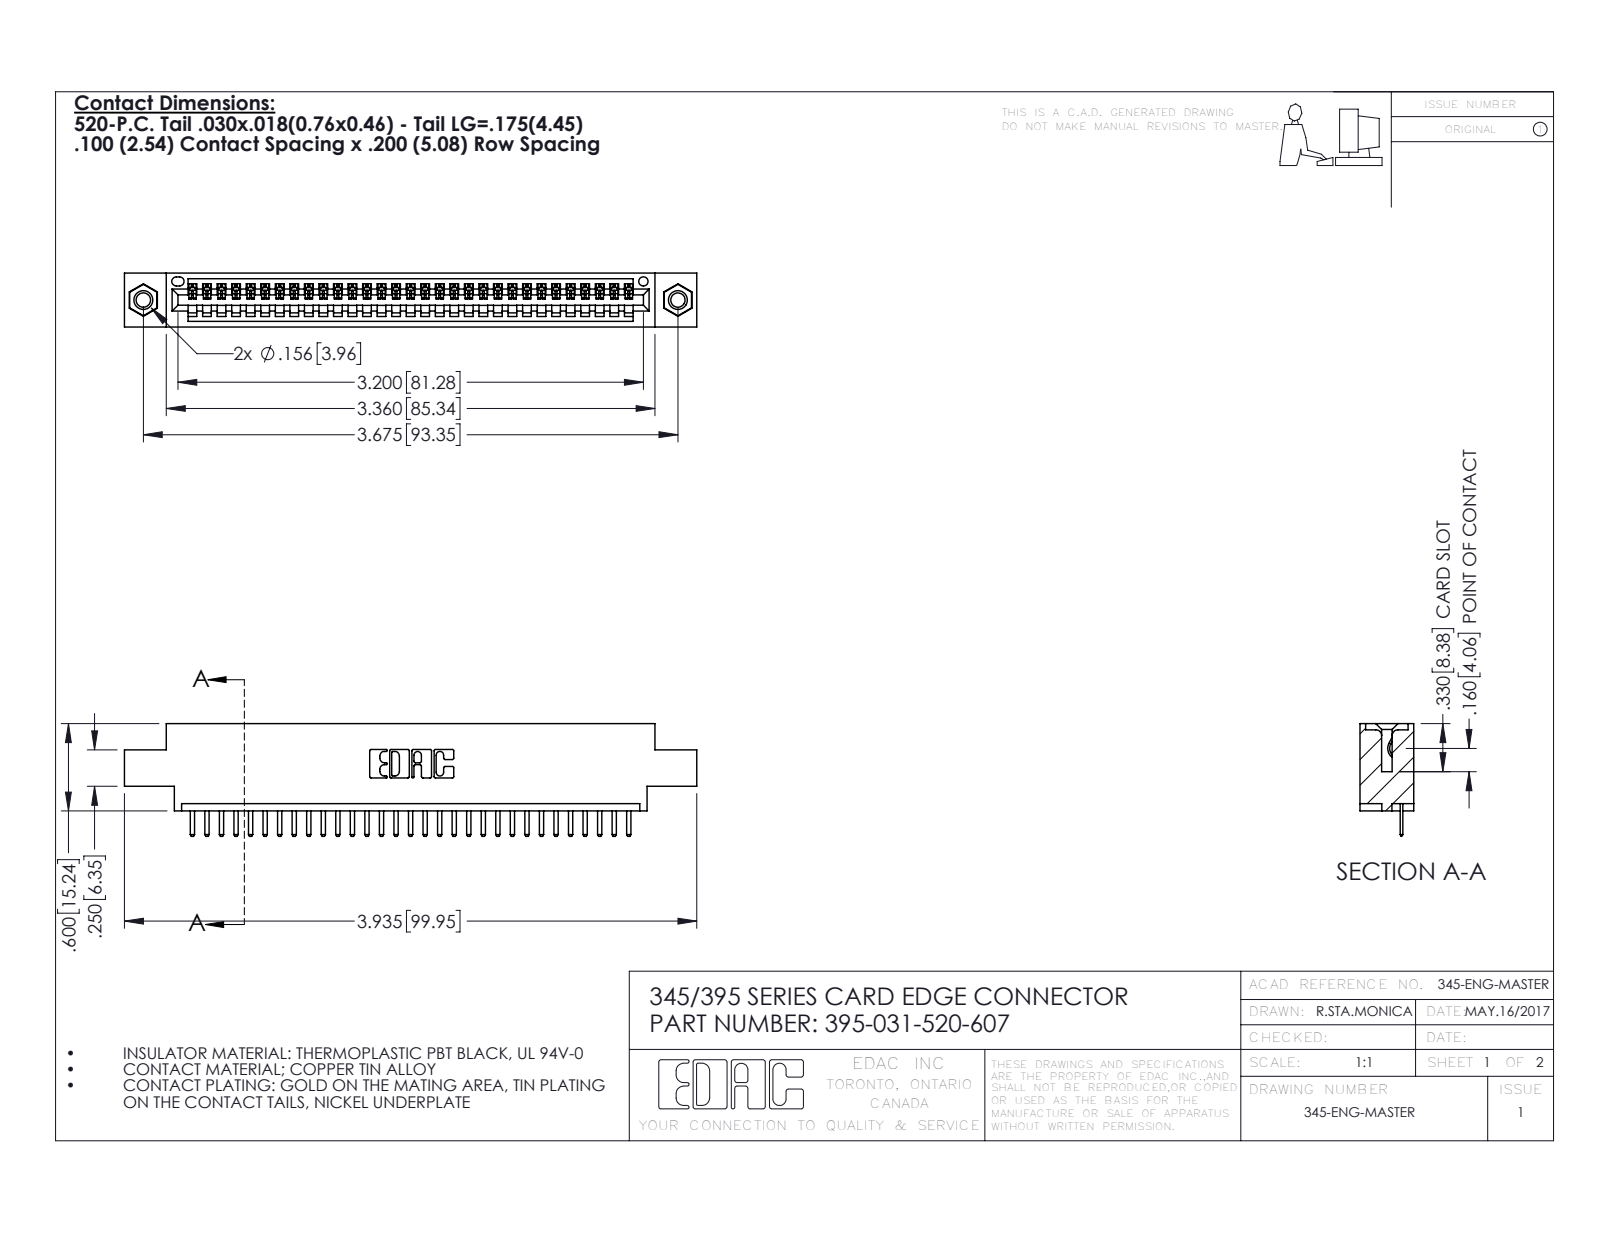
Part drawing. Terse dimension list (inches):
name: 345-250-001_345-250-005-103; 345 Part_0.170 Offset - 0.156 Dia-TI; 345-292-001_345-293-120; 395-031-520-607
written by: SolidWorks 2016 (CONFIG_CONTROL_DESIGN)
unit: in
bodies: 34 solids, 2112 faces (1418 planar, 678 cylindrical, 16 other)
size: 3.935 × 0.775 × 0.37
volume: 0.561 in³; area: 18.49 in²
holes: 2× ⌀0.098, 2× ⌀0.125, 2× ⌀0.156, 1× ⌀0.064
bosses: 2× ⌀0.155
rounds: 64× R0.01, 62× R0.006, 22× R0.01, 6× R0.007, 6× R0.031, 3× R0.026, 2× R0.031, 2× R0.04
face distances: 0.072, 0.298, 0.37, 0.2, 0.098, 0.272, 0.025, 0.225, 0.072, 0.175
hole spacings: 0.27, 3.44, 3.675
